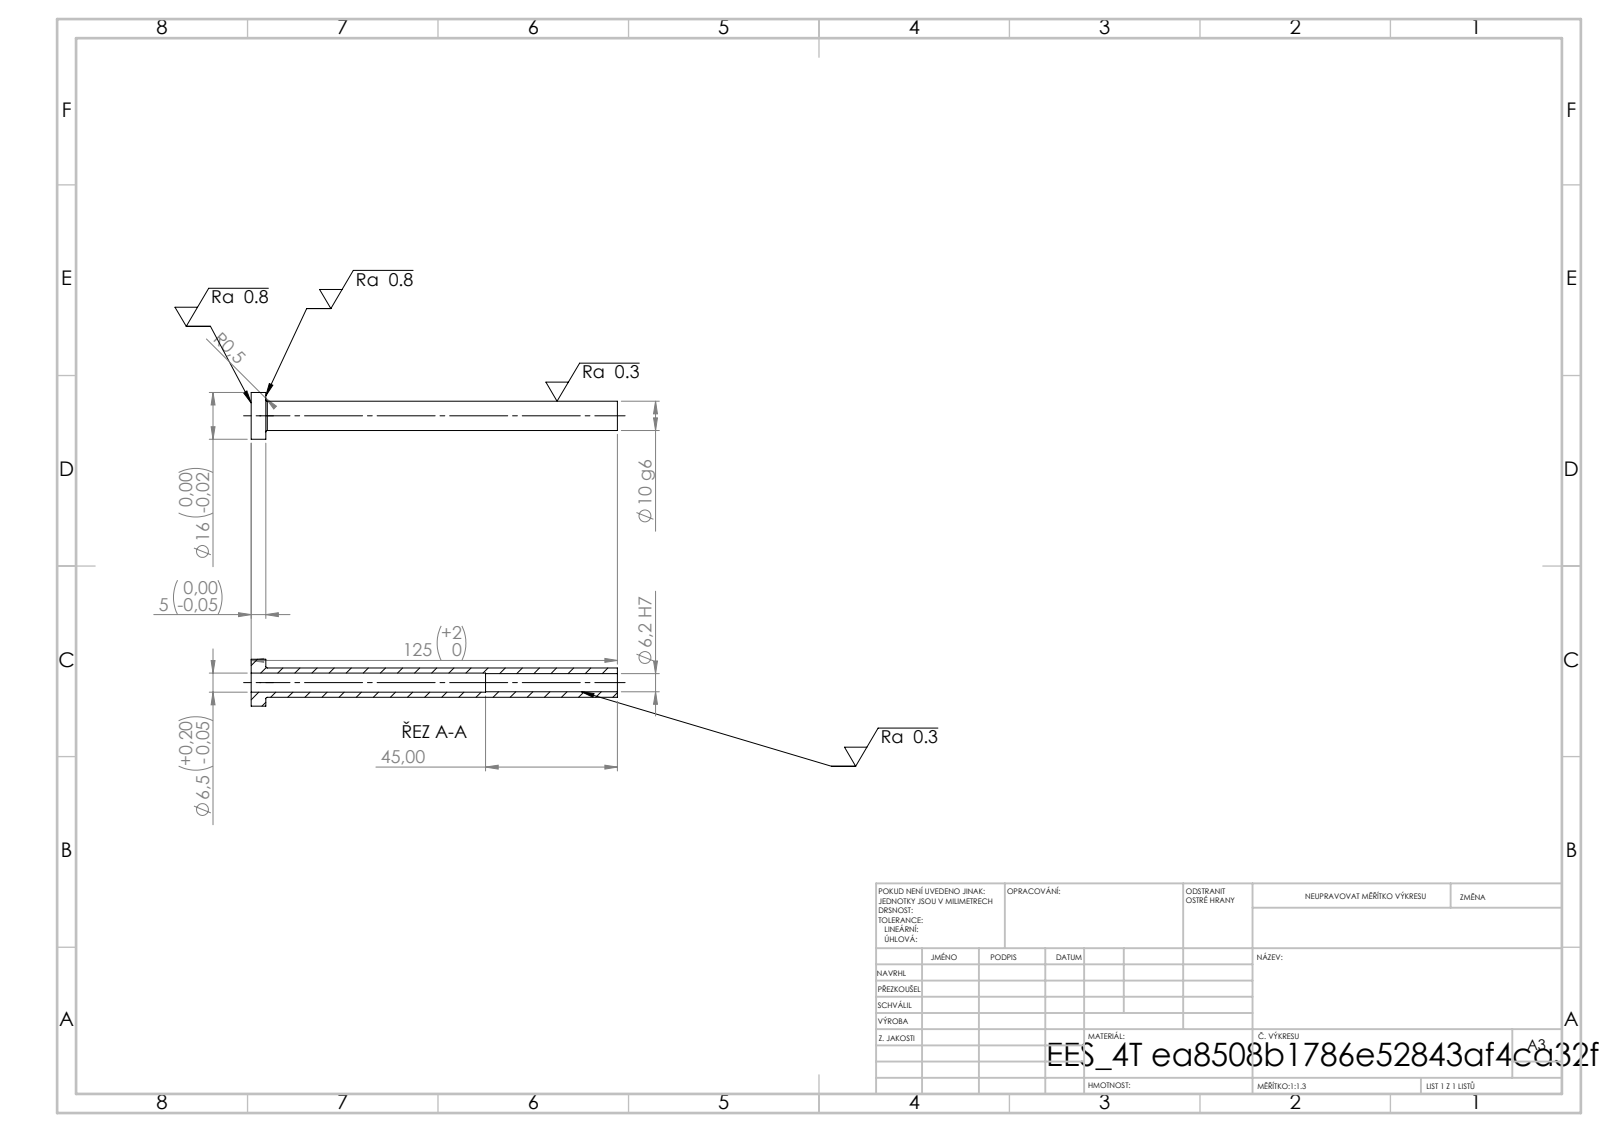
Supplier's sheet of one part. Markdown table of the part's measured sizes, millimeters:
| quantity | value |
| --- | --- |
| STEP written by | SolidWorks 2019 (CONFIG_CONTROL_DESIGN) |
| units | millimeters |
| bodies | 1 solid, 14 faces (4 planar, 8 cylindrical, 2 other) |
| overall size | 125 × 16 × 16 |
| volume | 6 419 mm³ |
| surface area | 6 866 mm² |
| round holes (diameter × count) | 6.2 × 1, 6.5 × 1 |
| round bosses / shafts (diameter × count) | 16 × 1, 10 × 1 |
| main face-to-face distances | 5, 125, 120, 80, 75, 45 |
